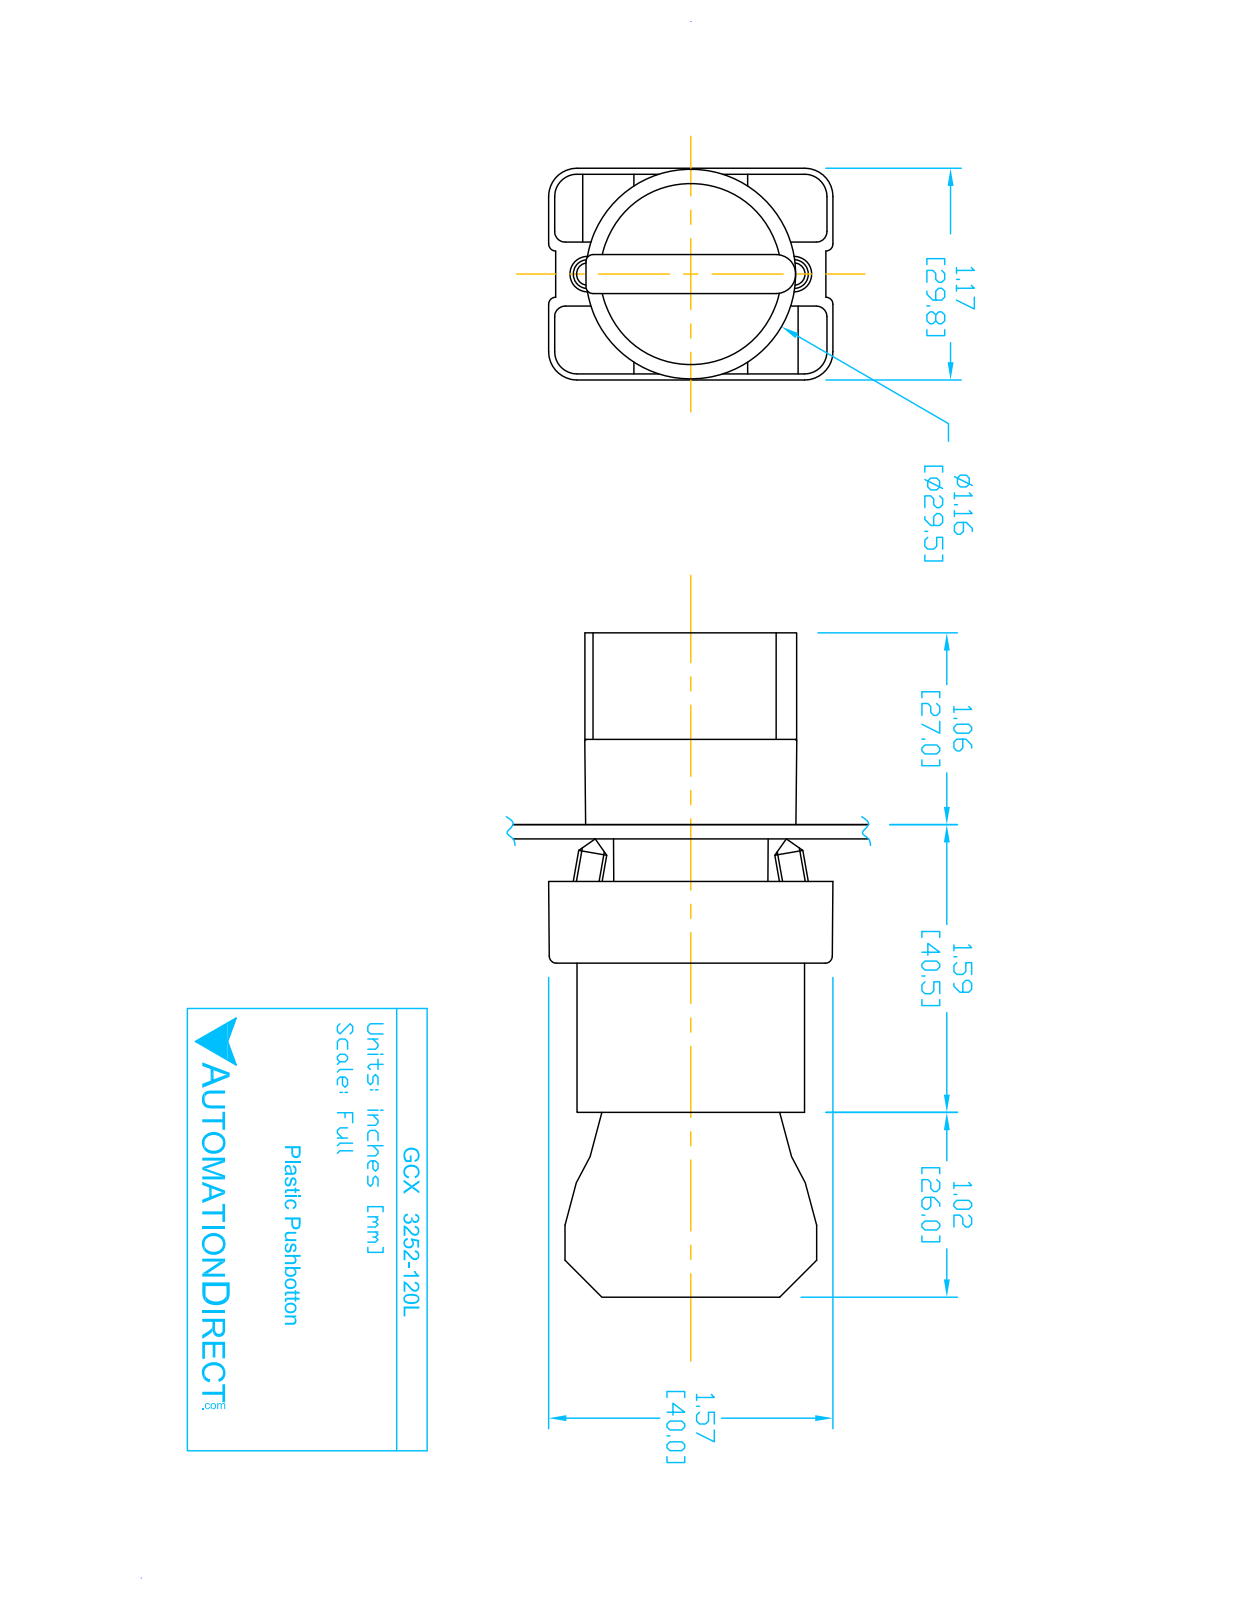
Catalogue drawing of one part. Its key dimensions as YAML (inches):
part_name: "ECX3029-2; ecx1040; GCX3252L OPERATOR; ECX1050 (+1 more)"
step_written_by: "SolidWorks 2016 (AUTOMOTIVE_DESIGN)"
units: inches
bodies: {solids: 8, faces: 445, planar: 263, cylindrical: 151, other: 31}
overall_size: [3.653, 1.581, 1.177]
volume: 2.799
surface_area: 39
round_holes:
  - {diameter: 0.079, count: 2}
  - {diameter: 0.124, count: 2}
  - {diameter: 0.13, count: 2}
  - {diameter: 0.087, count: 1}
  - {diameter: 0.197, count: 1}
  - {diameter: 0.469, count: 1}
  - {diameter: 0.878, count: 1}
  - {diameter: 0.888, count: 1}
  - {diameter: 1.024, count: 1}
round_bosses_or_shafts:
  - {diameter: 0.157, count: 4}
  - {diameter: 1.175, count: 1}
  - {diameter: 1.004, count: 1}
  - {diameter: 0.945, count: 1}
  - {diameter: 0.856, count: 1}
  - {diameter: 0.78, count: 1}
  - {diameter: 0.504, count: 1}
partial_cylinders:
  - {radius: 0.059, count: 24}
  - {radius: 0.041, count: 12}
  - {radius: 0.124, count: 12}
  - {radius: 0.157, count: 12}
  - {radius: 0.039, count: 9}
  - {radius: 0.128, count: 2}
  - {radius: 0.02, count: 1}
  - {radius: 0.063, count: 1}
face_to_face_distances: [0.827, 2.02, 1.193, 0.579, 1.244, 1.171, 0.472, 0.469, 0.031, 0.033]
hole_center_spacings: [0.236, 0.544, 0.472, 0.49]
